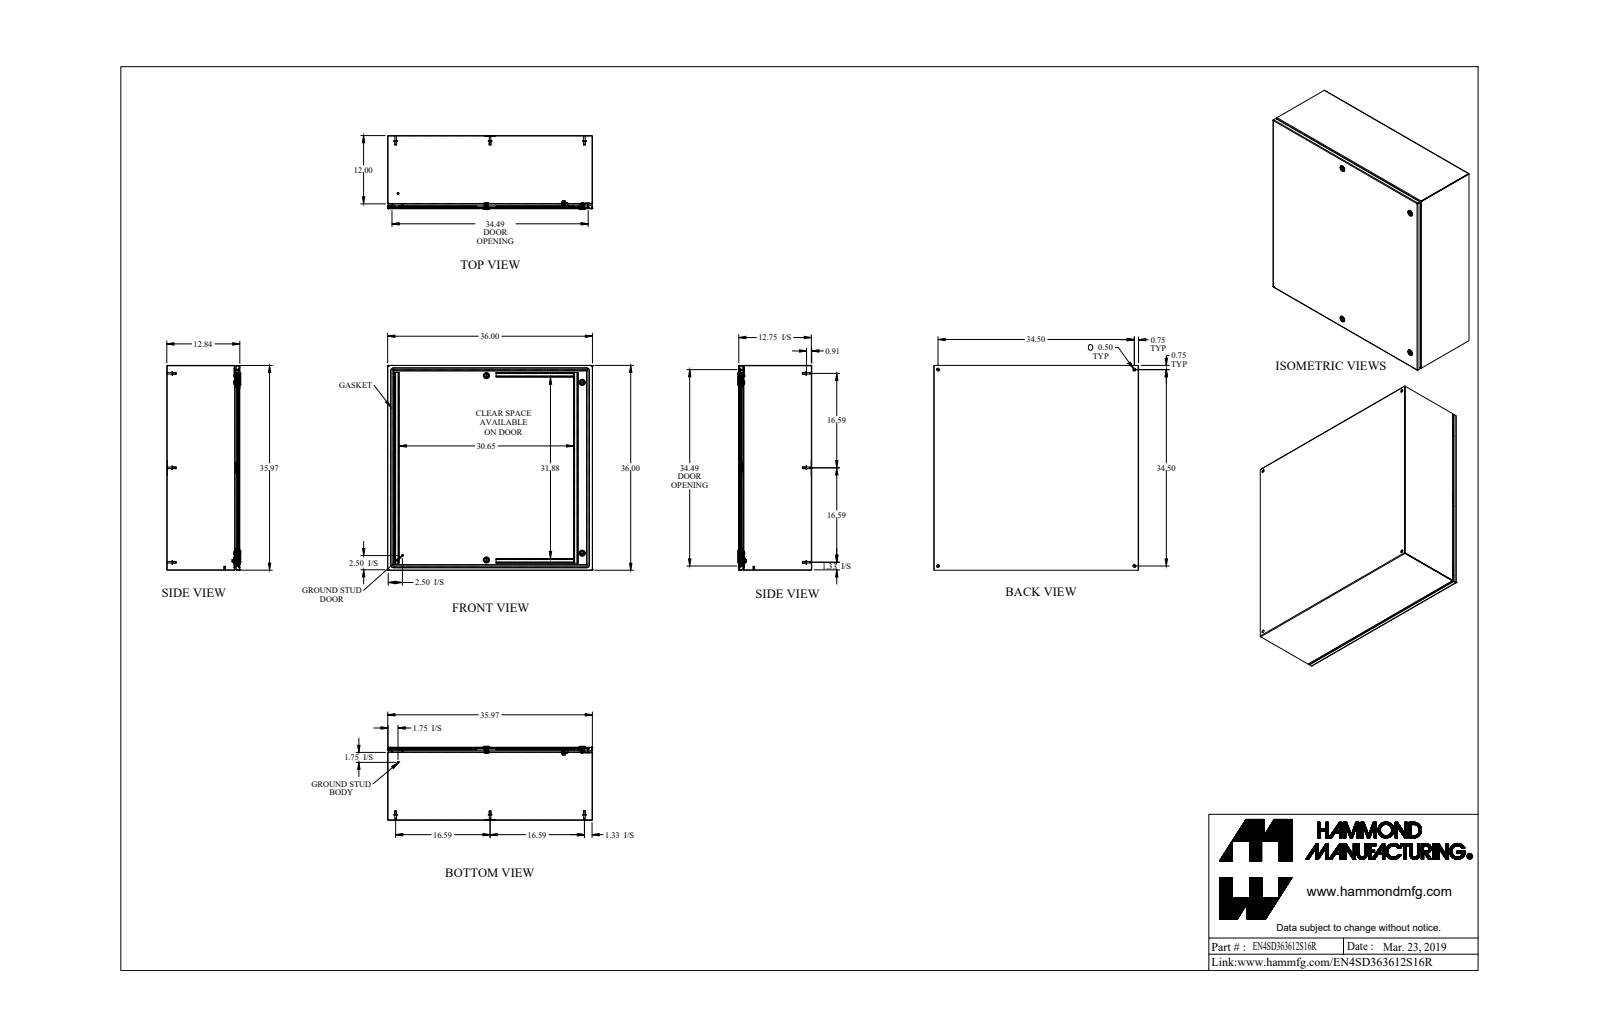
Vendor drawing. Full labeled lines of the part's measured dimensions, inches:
Part name (STEP PRODUCT): EN4SD363612S16R
STEP written by: SolidWorks 2019 (AUTOMOTIVE_DESIGN)
Units: inches
Bodies: 57 solids, 1495 faces (769 planar, 487 cylindrical, 239 other)
Overall size (bounding box): 36 × 36 × 13.002
Volume: 356 in³ · Surface area: 10 039 in²
Round holes (diameter × count): ⌀0.5 ×8, ⌀0.197 ×4, ⌀0.387 ×4, ⌀0.63 ×4, ⌀0.768 ×4, ⌀0.172 ×1, ⌀0.196 ×1, ⌀0.24 ×1, ⌀0.242 ×1, ⌀0.275 ×1, ⌀0.375 ×1
Round bosses / shafts (diameter × count): ⌀0.313 ×10, ⌀0.625 ×8, ⌀0.275 ×8, ⌀0.625 ×5, ⌀1.1 ×4, ⌀0.236 ×4, ⌀0.525 ×3, ⌀0.785 ×2
Partial cylindrical surfaces — rounded edges, fillets, slot ends (radius × count): R0.01 ×24, R0.048 ×24, R0.036 ×18, R0.108 ×18, R0.062 ×10, R0.094 ×10, R0.25 ×10, R0.016 ×9
Main face-to-face distances: 0.072, 12.77, 35.928, 12.698, 12.842, 35.856, 36, 0.842, 11.928, 0.038
Hole centre spacings: 34.5, 2.488, 16.634, 16.88, 17.931, 32.267, 33.515, 35.444
